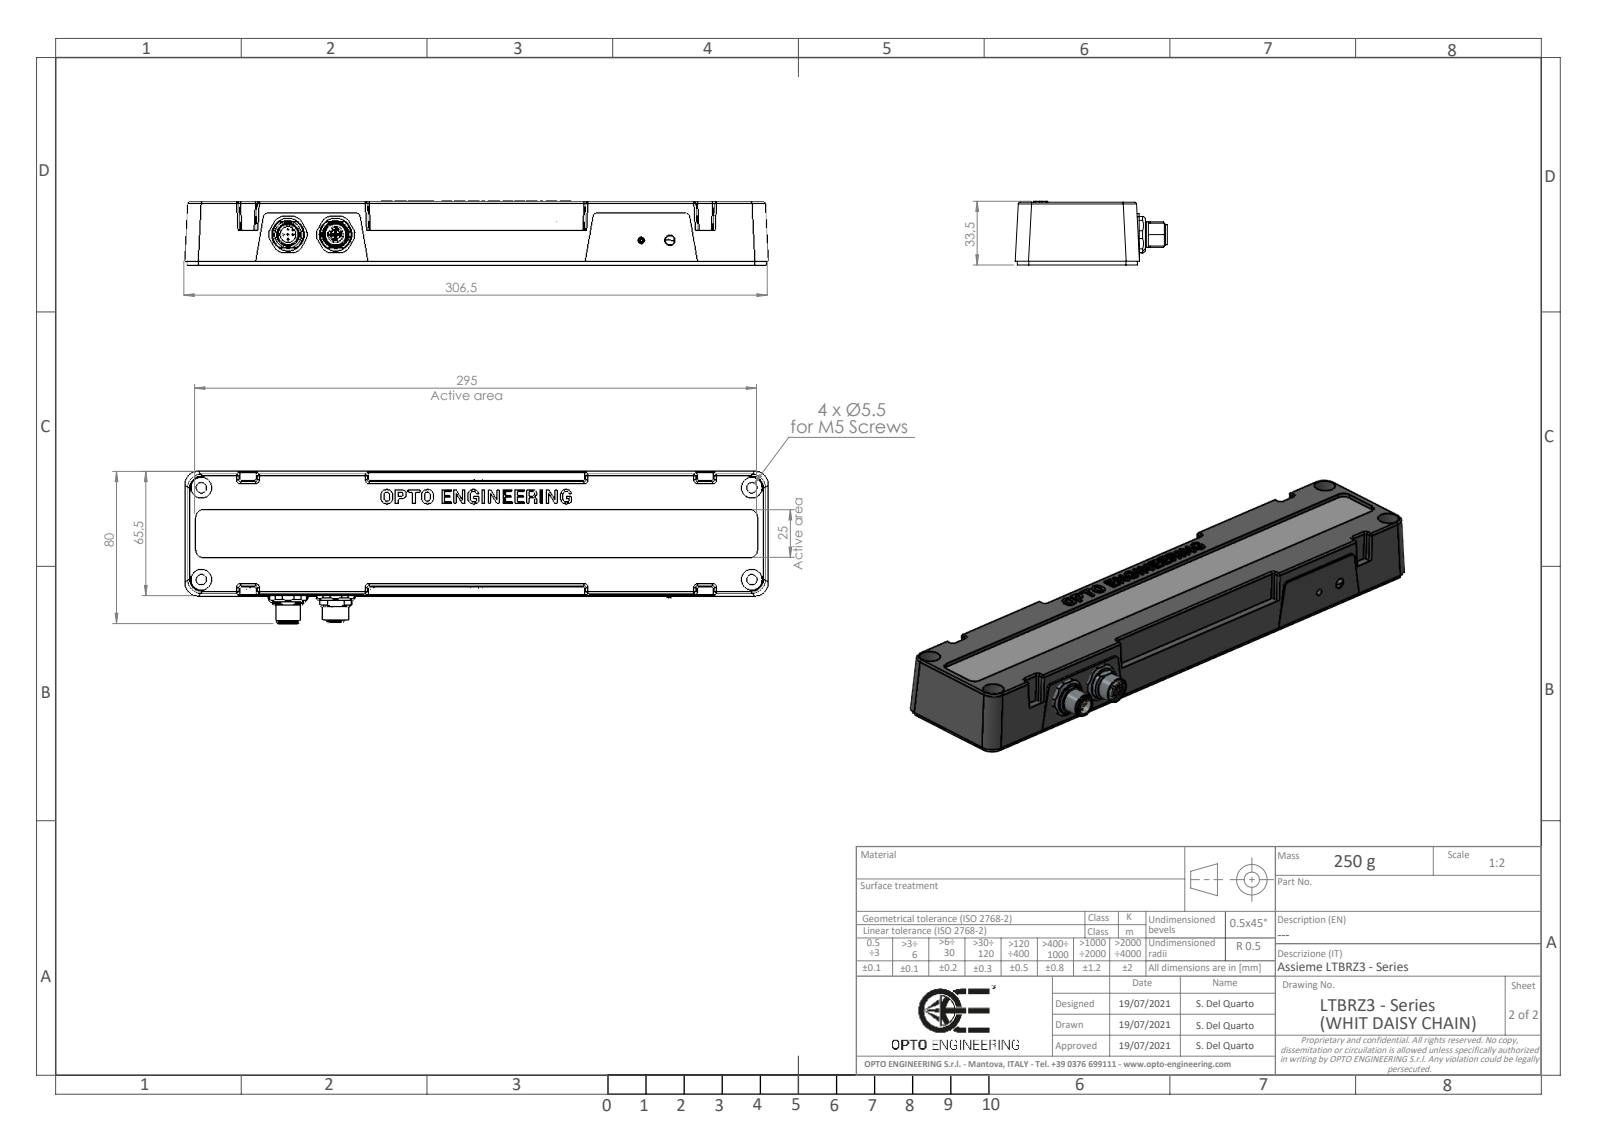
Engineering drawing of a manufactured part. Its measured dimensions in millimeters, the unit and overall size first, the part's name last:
Units: millimetres
Overall size (bounding box): 306.25 × 79.88 × 33.5
Round holes (diameter × count): ⌀1.5 ×5, ⌀5.5 ×5, ⌀1.1 ×1, ⌀3.5 ×1, ⌀8.3 ×1, ⌀10.92 ×1, ⌀12.3 ×1
Round bosses / shafts (diameter × count): ⌀5.5 ×10, ⌀1 ×5, ⌀13.4 ×1, ⌀12 ×1, ⌀10.5 ×1, ⌀8.2 ×1, ⌀2.2 ×1
Partial cylindrical surfaces — rounded edges, fillets, slot ends (radius × count): R0.55 ×60, R0.25 ×48, R1 ×36, R2 ×4, R4 ×4, R6 ×4, R7 ×4, R1.1 ×3
Main face-to-face distances: 31, 2, 33, 4, 3, 28, 30, 15, 19, 44
Hole centre spacings: 2.5, 3.54, 5, 25.12, 48, 289, 292.96, 15
Bodies: 0 solids, 626 faces (249 planar, 237 cylindrical, 140 other)
Part name (STEP PRODUCT): OELTBRZ300_ASSY_DAISY_CHAIN
STEP written by: SolidWorks 2020 (AUTOMOTIVE_DESIGN)
